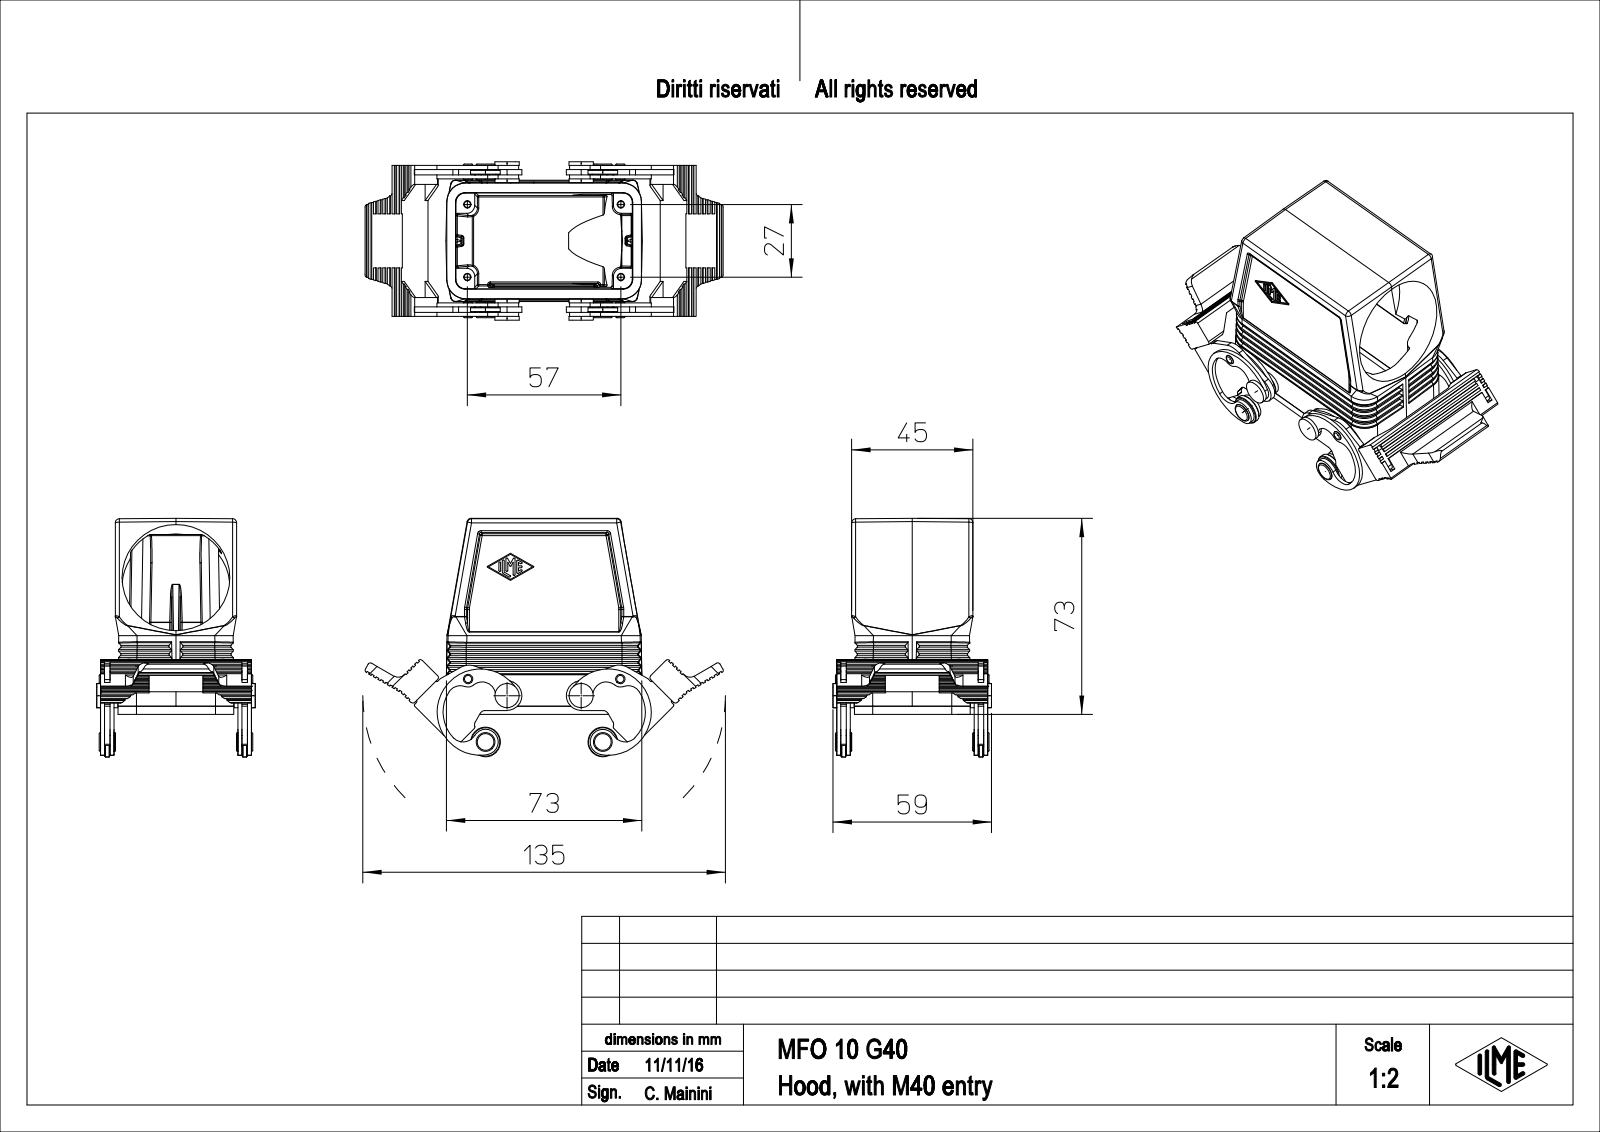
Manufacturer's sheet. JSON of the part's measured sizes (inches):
{"part_name": "MFO_10_G40", "step_written_by": "PTC Creo Elements/Direct Modeling 19.0E 27-Jun-2016 (C) Parametric Technology GmbH (AUTOMOTIVE_DESIGN)", "units": "inches", "bodies": {"solids": 1, "faces": 1147, "planar": 610, "cylindrical": 342, "other": 195}, "overall_size": [5.235, 3.486, 2.315], "volume_in3": 5.497, "surface_area_in2": 83.29, "round_holes": [[0.108, 4], [0.197, 4], [0.122, 2], [0.157, 2], [1.575, 1]], "round_bosses_or_shafts": [[0.433, 2], [0.354, 2], [0.276, 2], [0.189, 2], [0.138, 2], [0.118, 2]], "partial_cylinders_radius": [[0.02, 24], [0.059, 16], [0.118, 12], [0.039, 10], [0.276, 10], [0.197, 6], [0.079, 4], [0.138, 4]], "face_to_face_distances": [0.079, 0.138, 2.008, 0.059, 1.693, 0.157, 0.039, 2.067, 2.146, 1.929], "hole_center_spacings": [0.62, 0.748, 0.752, 0.955, 1.063, 1.339, 1.341, 1.554]}
